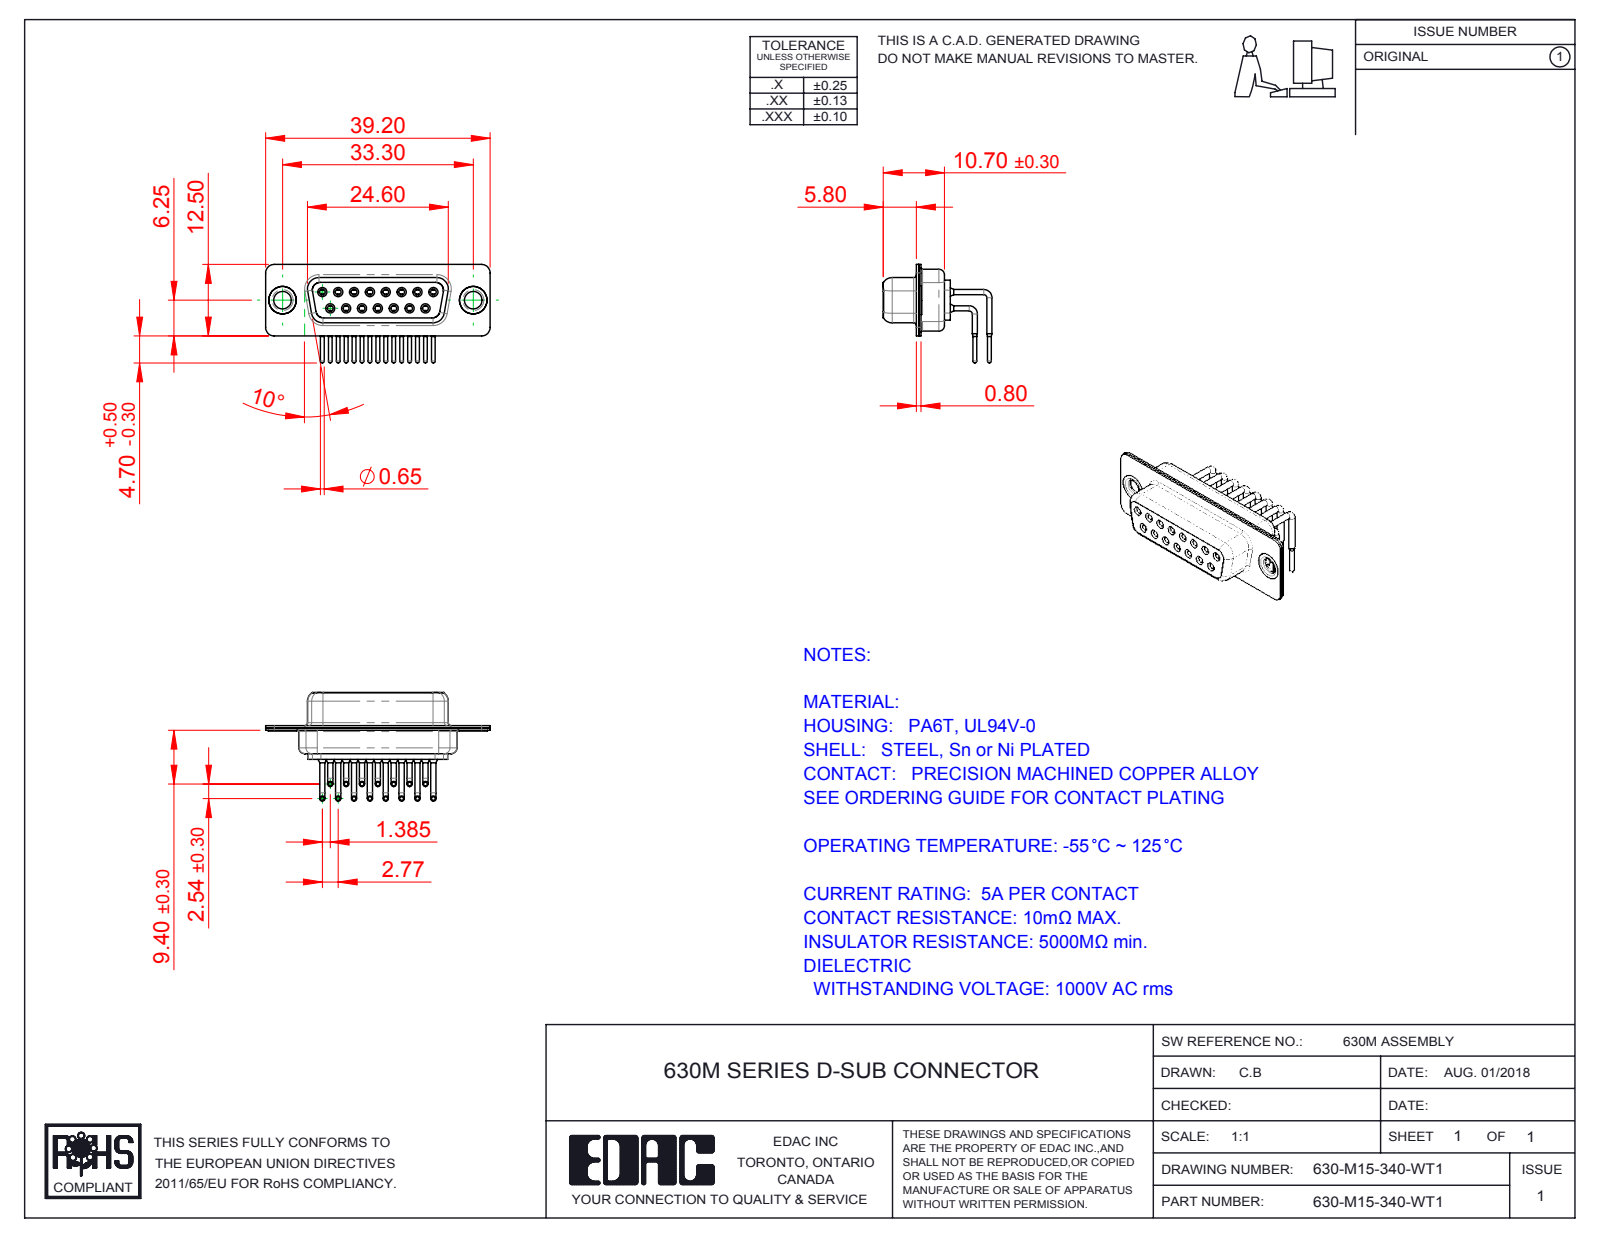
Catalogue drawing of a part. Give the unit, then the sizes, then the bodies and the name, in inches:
Units: inches
Overall size (bounding box): 1.543 × 0.748 × 0.677
Round holes (diameter × count): ⌀0.039 ×15, ⌀0.043 ×15, ⌀0.067 ×15, ⌀0.071 ×15, ⌀0.079 ×15, ⌀0.12 ×2, ⌀0.157 ×2, ⌀0.189 ×2
Round bosses / shafts (diameter × count): ⌀0.035 ×30, ⌀0.063 ×15, ⌀0.059 ×15, ⌀0.026 ×15, ⌀0.197 ×2, ⌀0.193 ×2, ⌀0.14 ×2
Partial cylindrical surfaces — rounded edges, fillets, slot ends (radius × count): R0.059 ×16, R0.079 ×12, R0.053 ×8, R0.063 ×8, R0.01 ×4, R0.02 ×4, R0.024 ×4, R0.026 ×4
Main face-to-face distances: 0.016, 0.057, 0.352, 0.244, 0.075, 0.335, 0.091, 0.018, 0.278, 0.033
Hole centre spacings: 0.124, 0.109, 0.218, 0.327, 0.436, 0.198, 0.198, 0.294
Volume: 0.152 in³ · Surface area: 9.926 in²
Bodies: 20 solids, 1048 faces (292 planar, 466 cylindrical, 290 other)
Part name (STEP PRODUCT): 630M Contact Row 2; 630M Thru Hole Rivet; 630-M15-340-WT1; 630M Shell Rear_15 Contacts (+3 more)
STEP written by: SolidWorks 2016 (CONFIG_CONTROL_DESIGN)
